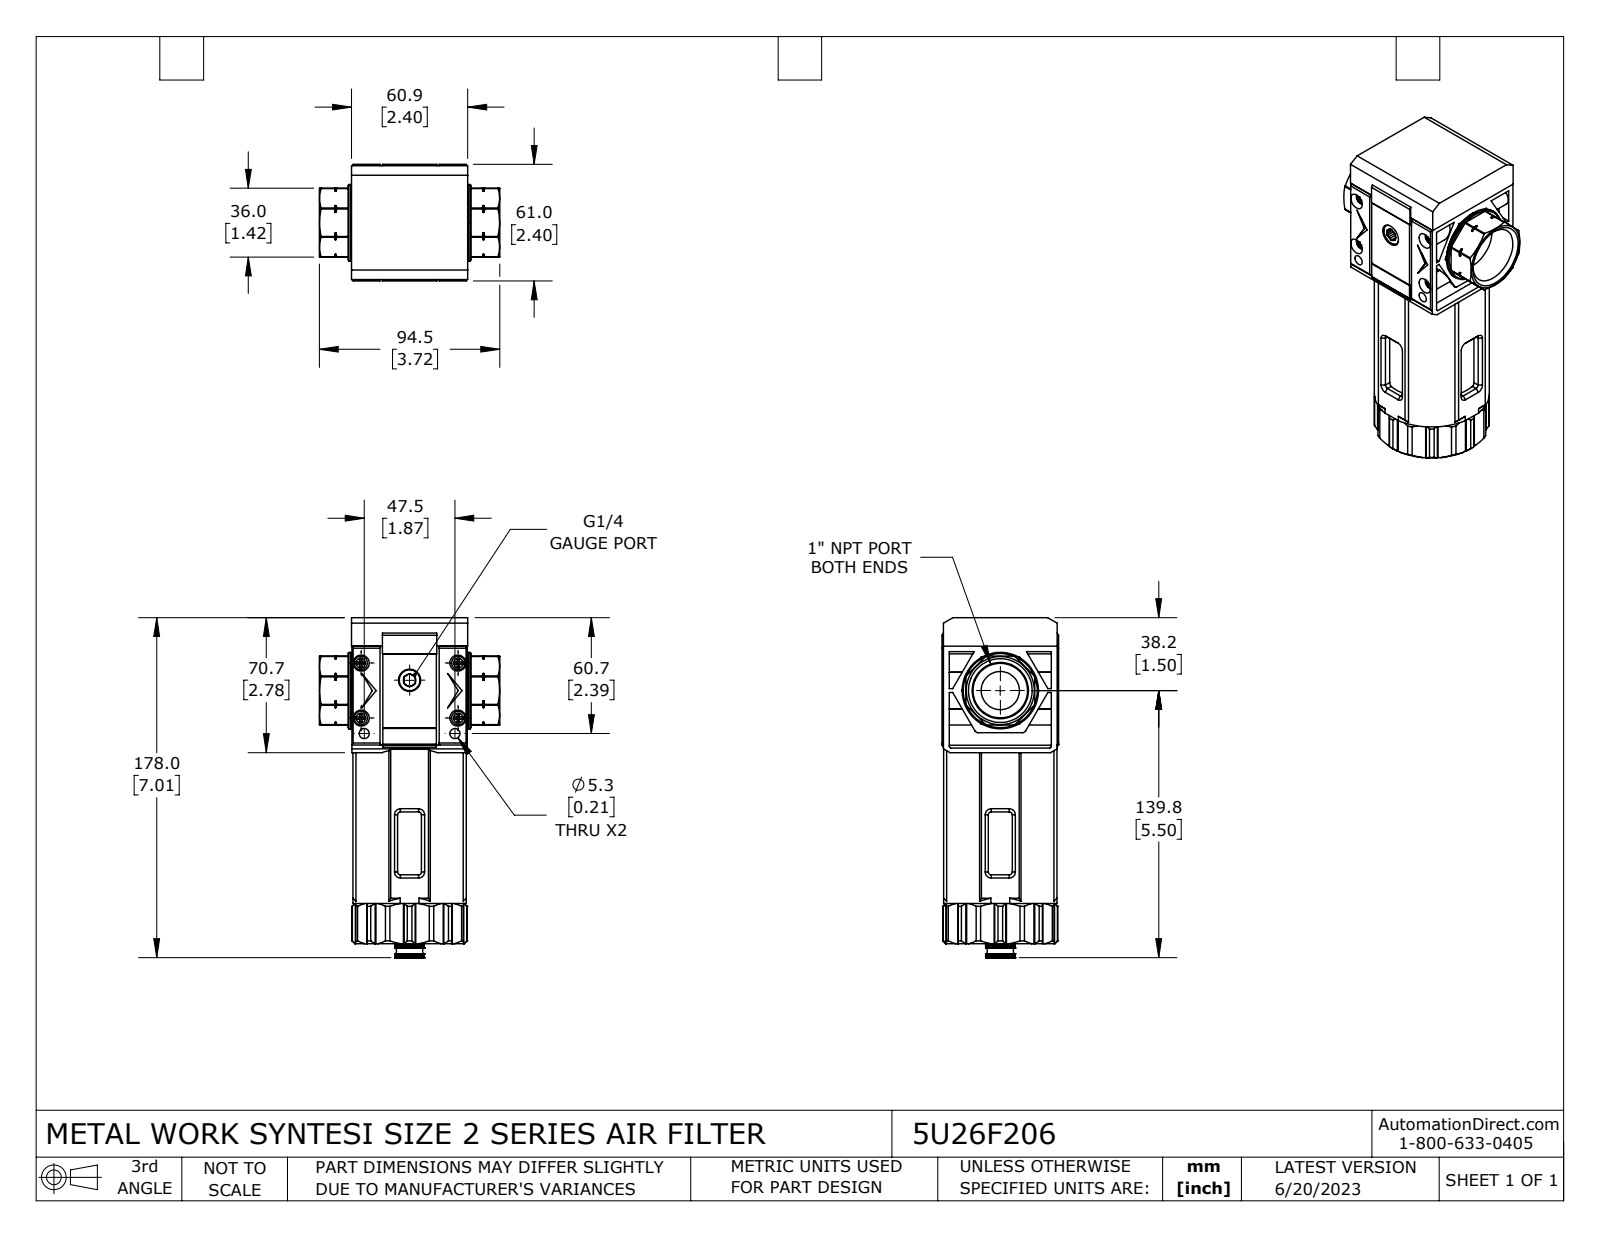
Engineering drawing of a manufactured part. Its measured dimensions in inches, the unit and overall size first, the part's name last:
Units: inches
Overall size (bounding box): 7.008 × 3.72 × 2.402
Round holes (diameter × count): ⌀0.128 ×4, ⌀0.165 ×4, ⌀0.331 ×4, ⌀0.209 ×2, ⌀0.126 ×1, ⌀0.276 ×1, ⌀0.343 ×1, ⌀0.457 ×1, ⌀0.787 ×1, ⌀1.26 ×1, ⌀1.929 ×1, ⌀1.969 ×1
Round bosses / shafts (diameter × count): ⌀0.276 ×4, ⌀0.189 ×4, ⌀0.15 ×4, ⌀1.575 ×1, ⌀1.378 ×1, ⌀1.248 ×1, ⌀1.035 ×1, ⌀0.925 ×1
Partial cylindrical surfaces — rounded edges, fillets, slot ends (radius × count): R0.02 ×16, R0.059 ×8, R0.191 ×4, R0.008 ×2, R0.079 ×2, R0.242 ×2, R0.12 ×1, R0.276 ×1
Main face-to-face distances: 2.39, 5.303, 3.205, 2.098, 0.591, 2.689, 1.13, 5.894, 2.193, 2.402
Hole centre spacings: 0.325, 1.057, 1.134, 1.265, 1.443, 1.454, 1.957, 1.992
Volume: 24.54 in³ · Surface area: 198.9 in²
Bodies: 14 solids, 1590 faces (983 planar, 321 cylindrical, 286 other)
Part name (STEP PRODUCT): 5U26F206
STEP written by: SolidWorks 2021 (CONFIG_CONTROL_DESIGN)
